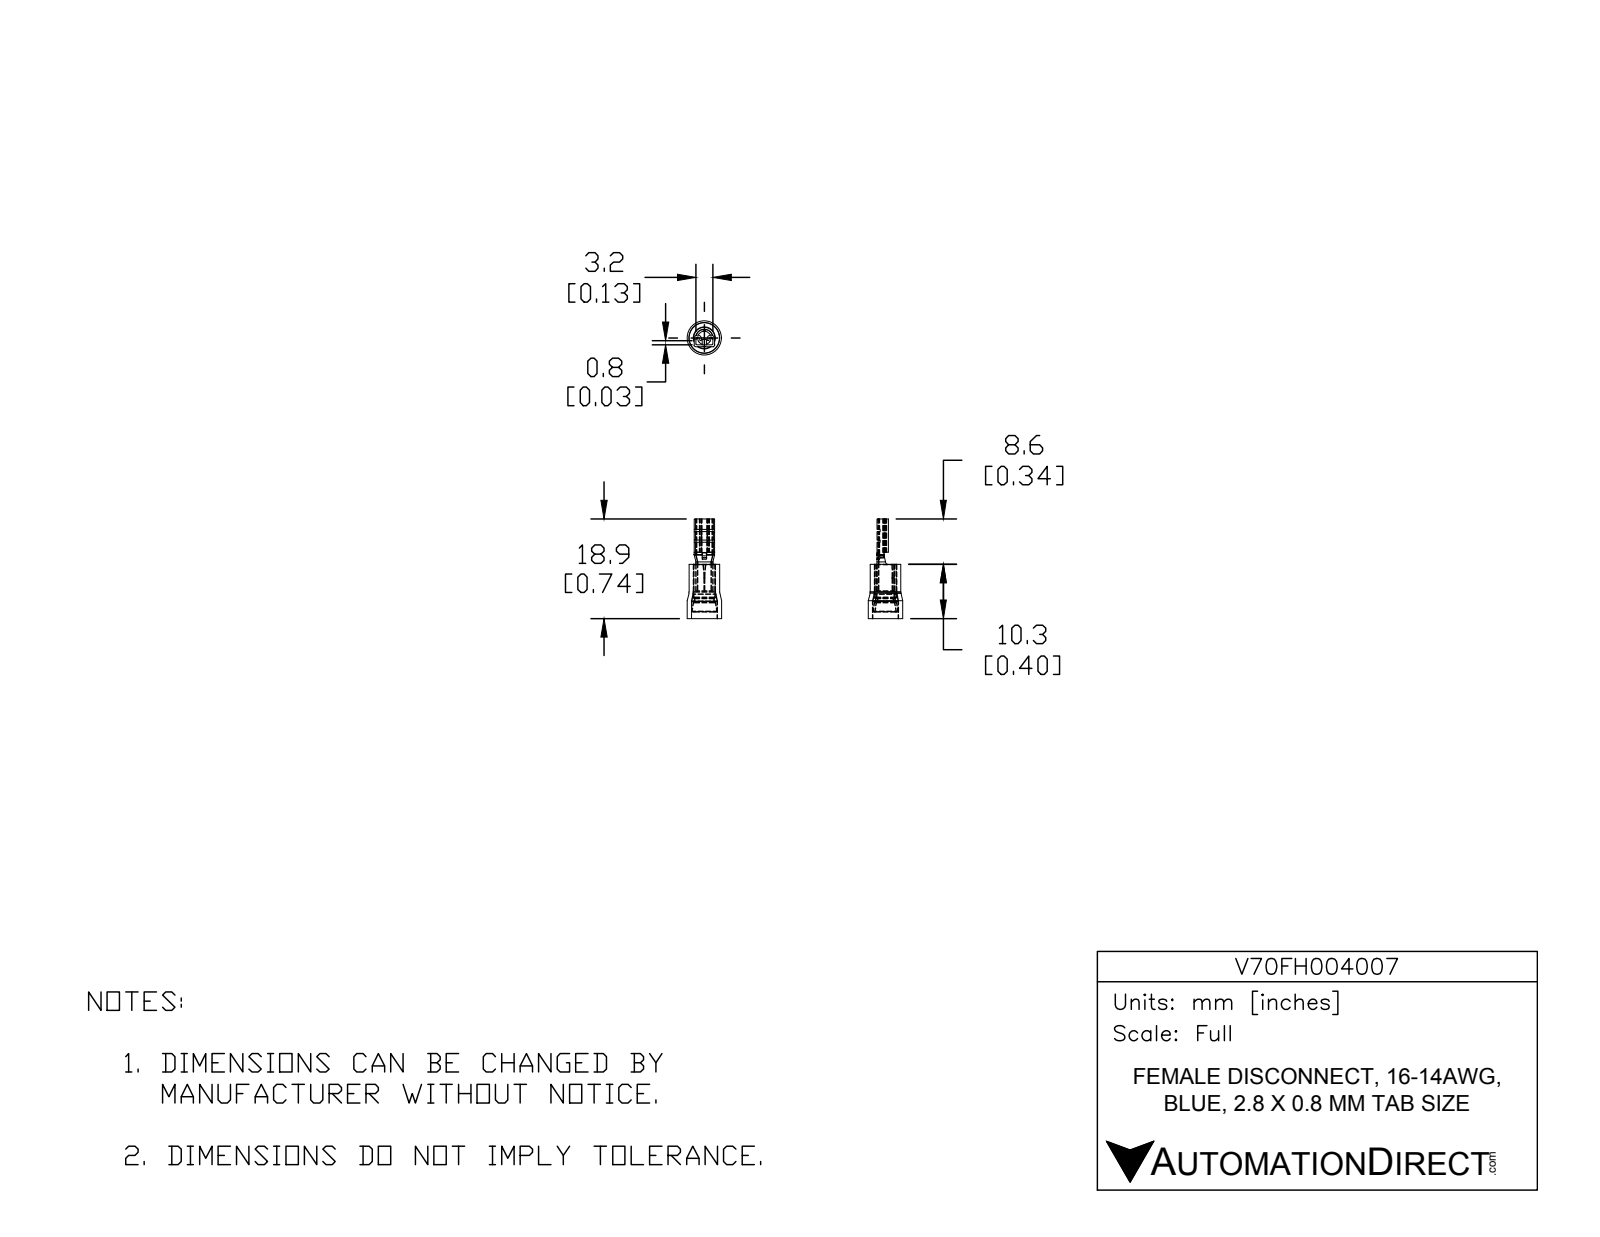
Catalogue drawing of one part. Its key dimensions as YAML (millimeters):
part_name: "V70FH004007"
step_written_by: "SolidWorks 2017 (AUTOMOTIVE_DESIGN)"
units: millimeters
bodies: {solids: 3, faces: 121, planar: 49, cylindrical: 38, other: 34}
overall_size: [18.86, 6.49, 6.49]
volume: 213
surface_area: 846
round_holes:
  - {diameter: 2.55, count: 1}
  - {diameter: 3.3, count: 1}
  - {diameter: 4.17, count: 1}
  - {diameter: 4.89, count: 1}
round_bosses_or_shafts:
  - {diameter: 6.49, count: 1}
  - {diameter: 5.77, count: 1}
  - {diameter: 4, count: 1}
  - {diameter: 3.25, count: 1}
partial_cylinders:
  - {radius: 0.12, count: 2}
  - {radius: 0.25, count: 2}
  - {radius: 0.35, count: 2}
  - {radius: 0.7, count: 2}
  - {radius: 15.72, count: 2}
  - {radius: 0.36, count: 1}
  - {radius: 0.5, count: 1}
  - {radius: 0.71, count: 1}
face_to_face_distances: [0.35, 0.36, 3.54, 10.26, 3.9, 2, 3.18, 10.2, 18.86, 8.66]
